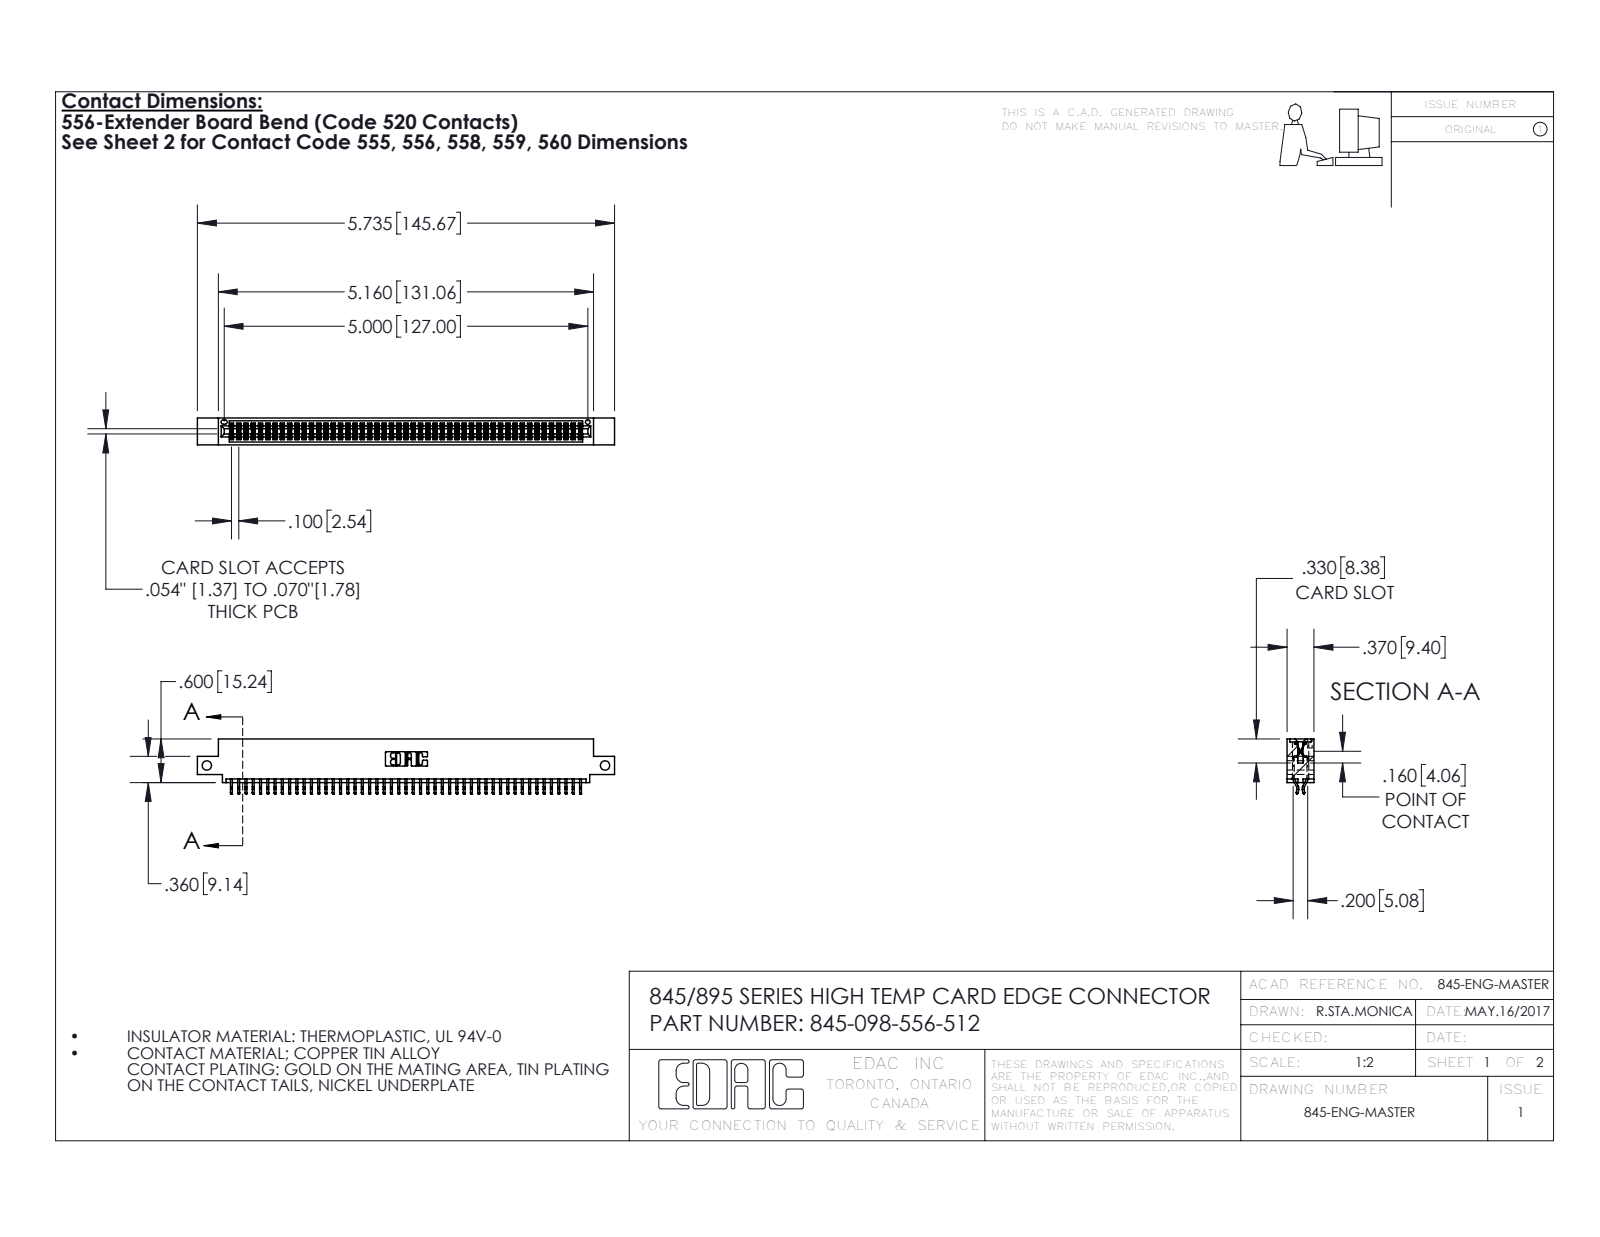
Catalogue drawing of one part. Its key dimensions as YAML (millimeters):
part_name: "345-098-556-512; 345 Part_0.110 Offset - Side Mount; 345-292-001_556 Tail"
step_written_by: "SolidWorks 2016 (CONFIG_CONTROL_DESIGN)"
units: millimeters
bodies: {solids: 99, faces: 5618, planar: 3710, cylindrical: 1908, other: 0}
overall_size: [145.7, 19.2, 9.4]
volume: 14000
surface_area: 20770
round_holes:
  - {diameter: 3.3, count: 2}
  - {diameter: 1.6, count: 1}
partial_cylinders:
  - {radius: 0.2, count: 147}
  - {radius: 0.3, count: 22}
  - {radius: 0.2, count: 6}
  - {radius: 0.8, count: 6}
  - {radius: 0.7, count: 3}
  - {radius: 0.3, count: 2}
  - {radius: 0.4, count: 2}
  - {radius: 0.5, count: 2}
face_to_face_distances: [7.6, 1.8, 9.4, 5.1, 0.6, 2.5, 6.9, 5.7, 4.4, 3.8]
hole_center_spacings: [139.1]
